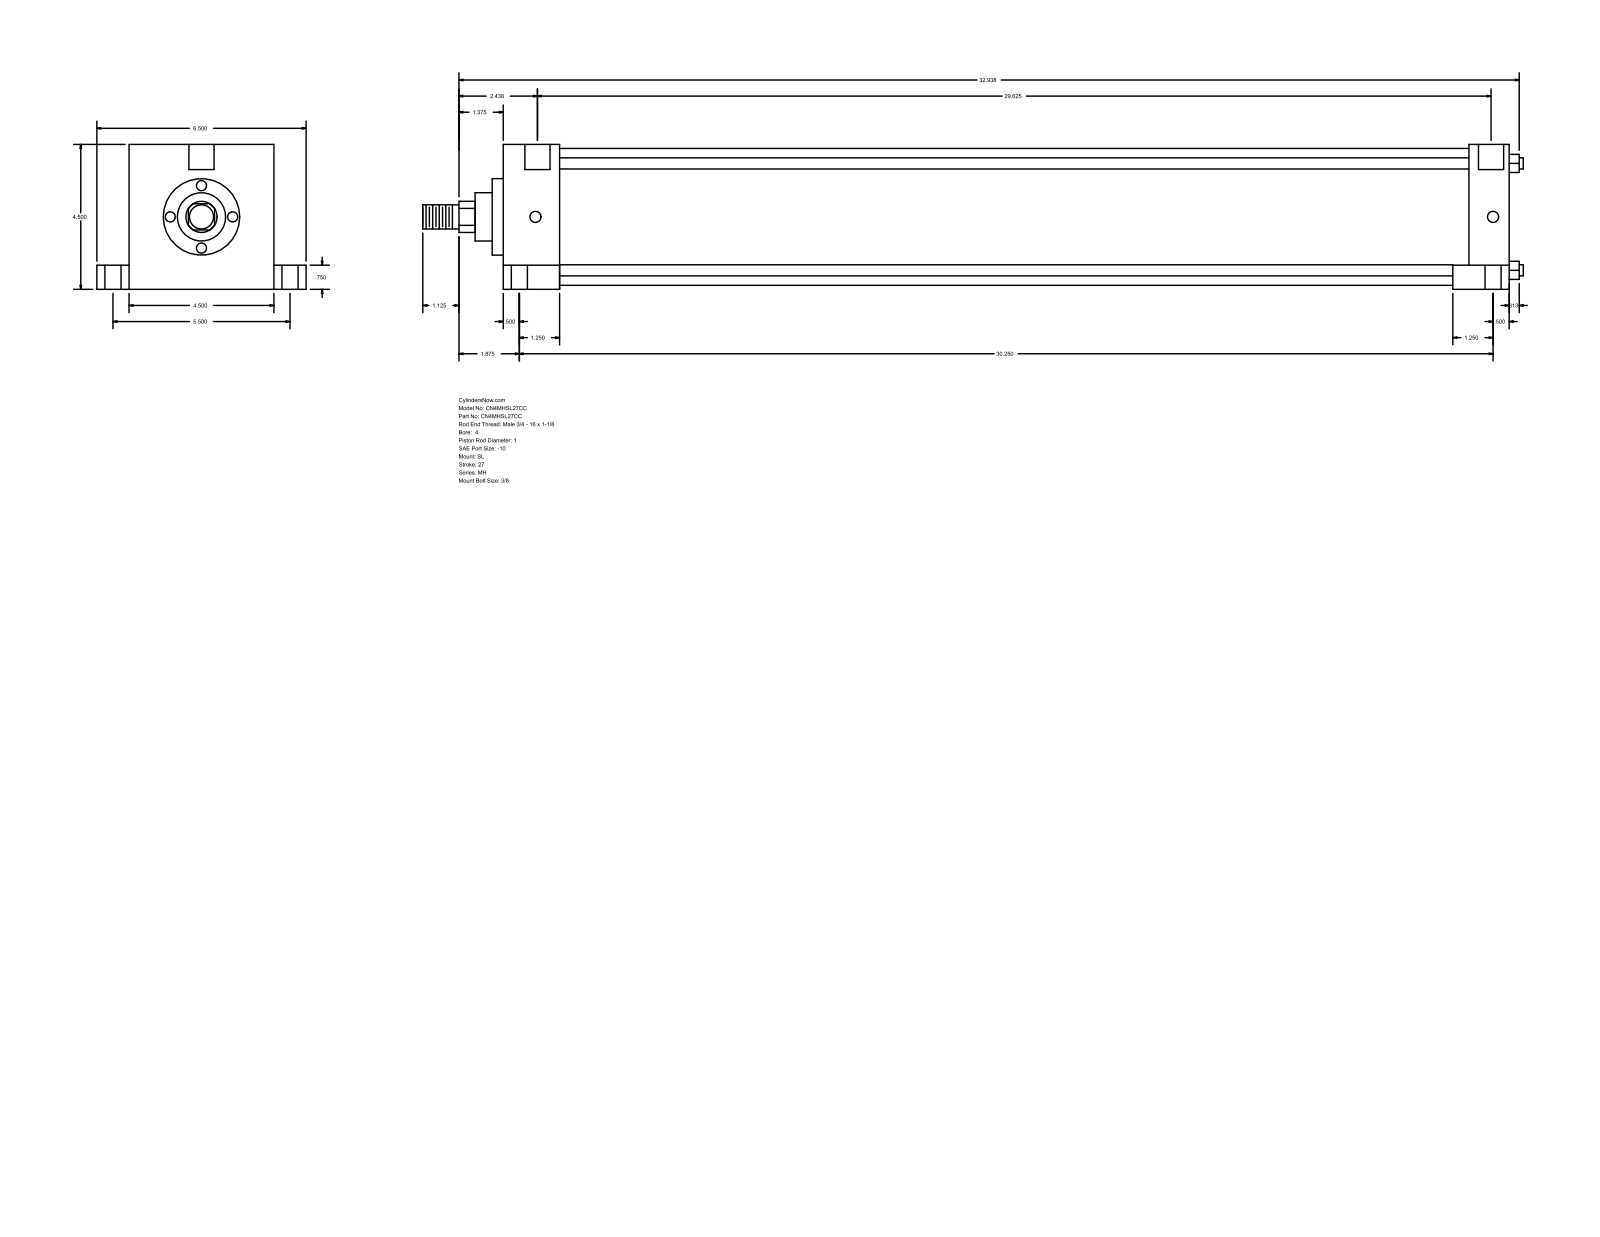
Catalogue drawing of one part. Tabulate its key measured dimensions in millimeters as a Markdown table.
| quantity | value |
| --- | --- |
| part name | MH_SL__0400_1 |
| STEP written by | GSSL Pune (CONFIG_CONTROL_DESIGN) |
| units | millimeters |
| bodies | 0 solids, 110 faces (77 planar, 33 cylindrical, 0 other) |
| overall size | 868.36 × 165.1 × 114.3 |
| round holes (diameter × count) | 8.73 × 4, 12.7 × 4, 19.05 × 4, 19.84 × 2 |
| round bosses / shafts (diameter × count) | 8.76 × 4, 107.95 × 1, 60.33 × 1, 38.1 × 1, 25.4 × 1, 19.05 × 1 |
| partial cylindrical surfaces (radius × count) | 12.29 × 1 |
| main face-to-face distances | 114.3, 793.75, 44.46, 749.29, 762, 717.54, 31.75, 25.4, 139.7, 19.05 |
| hole center spacings | 69.85, 69.87, 71, 71.3, 139.7, 755.65, 757.3, 758.87 |
